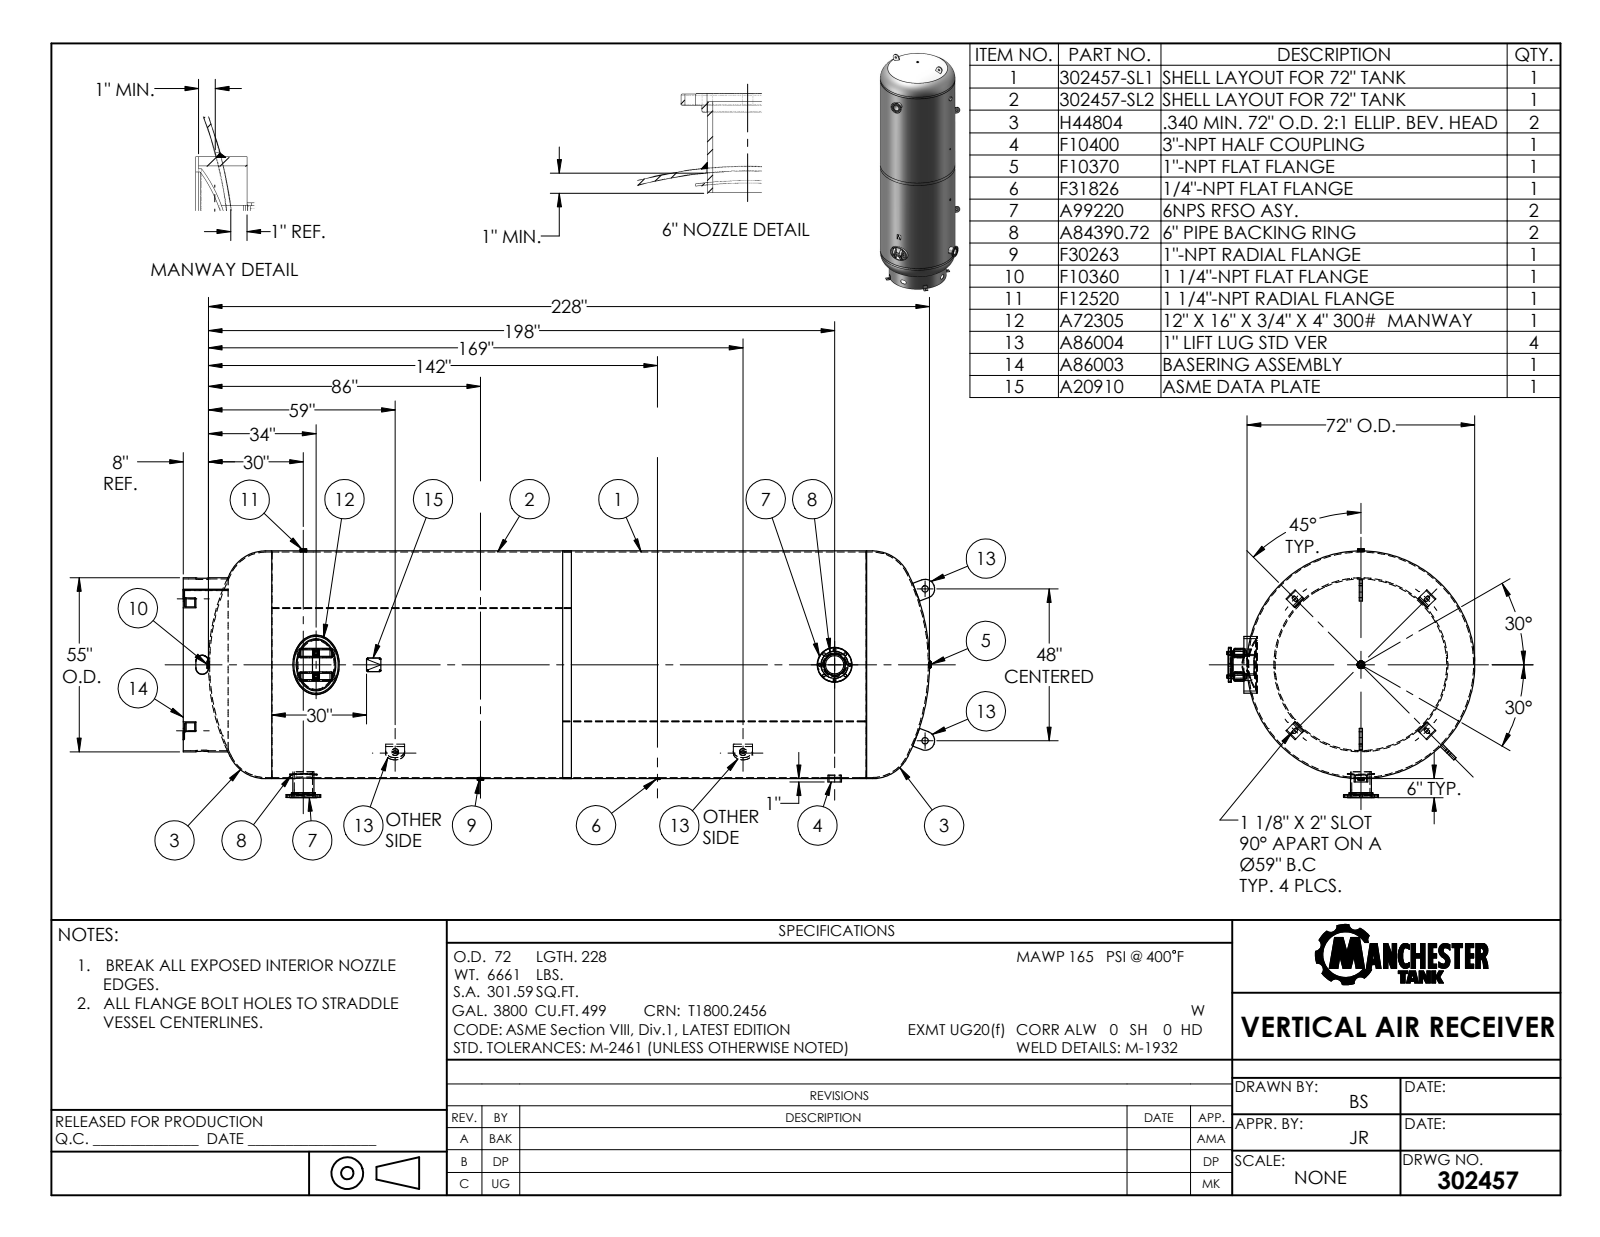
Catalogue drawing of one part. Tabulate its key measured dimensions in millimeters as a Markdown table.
| quantity | value |
| --- | --- |
| part name | 302457 |
| STEP written by | SolidWorks 2011 (CONFIG_CONTROL_DESIGN) |
| units | millimeters |
| bodies | 0 solids, 354 faces (126 planar, 163 cylindrical, 65 other) |
| overall size | 6041.8 × 2001.5 × 1990.6 |
| round holes (diameter × count) | 22.2 × 16, 50.8 × 4, 42.2 × 2, 146.3 × 2, 170.7 × 2, 13.7 × 1, 33.4 × 1, 33.4 × 1, 88.9 × 1, 1378 × 1, 1809.8 × 1 |
| round bosses / shafts (diameter × count) | 279.4 × 2, 215.9 × 2, 168.3 × 2, 60.3 × 2, 25.4 × 2, 1828.8 × 1, 1397 × 1, 108 × 1 |
| partial cylindrical surfaces (radius × count) | 9.5 × 11, 14.3 × 6, 12.7 × 4, 33.5 × 4, 74.6 × 4, 74.6 × 4, 14.3 × 2, 150.3 × 1 |
| main face-to-face distances | 25.4, 3054, 19.1, 3073.1, 2355.9, 2336.8, 717.2, 2419.4, 2438.4, 4775.2 |
| hole center spacings | 170.6, 92.3, 120.7, 222.9, 120.7, 120.7, 92.4, 222.9 |
